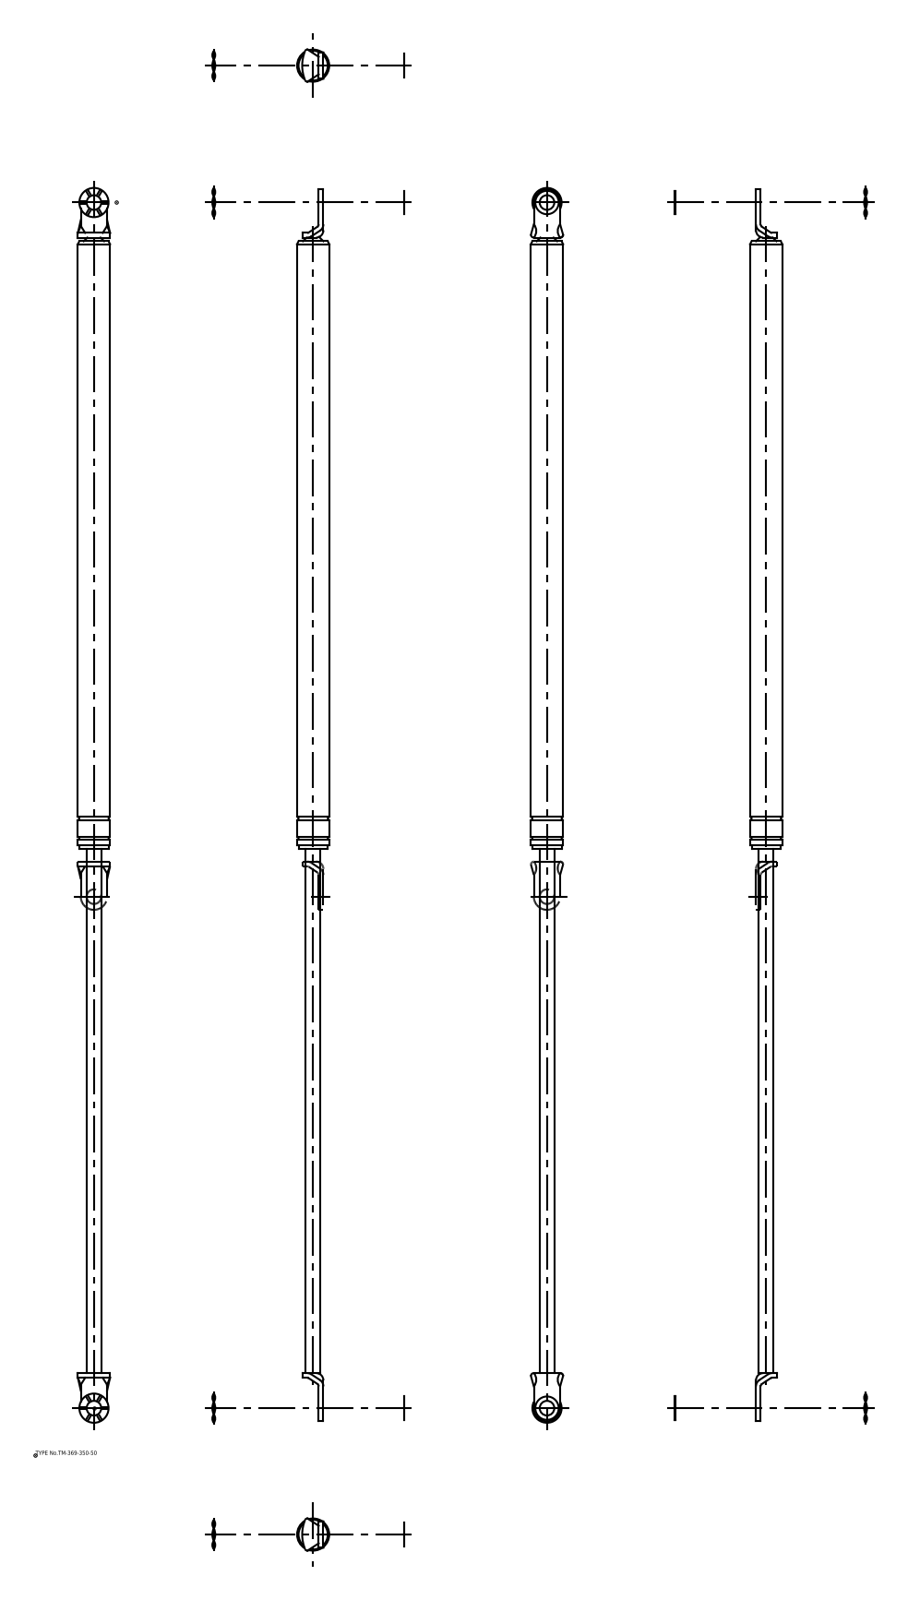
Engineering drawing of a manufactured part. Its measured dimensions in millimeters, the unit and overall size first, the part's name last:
Units: millimetres
Overall size (bounding box): 845 × 22.5 × 22.5
Round holes (diameter × count): ⌀10 ×2
Round bosses / shafts (diameter × count): ⌀20 ×3, ⌀16 ×2, ⌀22.5 ×1, ⌀22 ×1, ⌀10 ×1
Partial cylindrical surfaces — rounded edges, fillets, slot ends (radius × count): R4.4 ×2, R5 ×2, R9 ×2, R26.32 ×1
Main face-to-face distances: 3.2, 2, 5.2, 5.7, 780.2, 3.7, 0.5, 421.2, 362.2, 783.4
Hole centre spacings: 825
Volume: 191 849 mm³ · Surface area: 46 452 mm²
Bodies: 6 solids, 95 faces (43 planar, 44 cylindrical, 8 other)
Part name (STEP PRODUCT): ウェーブワッシャー; ワッシャー; 本体; 本体_div
STEP written by: spGate 16.7.1 (AUTOMOTIVE_DESIGN)
